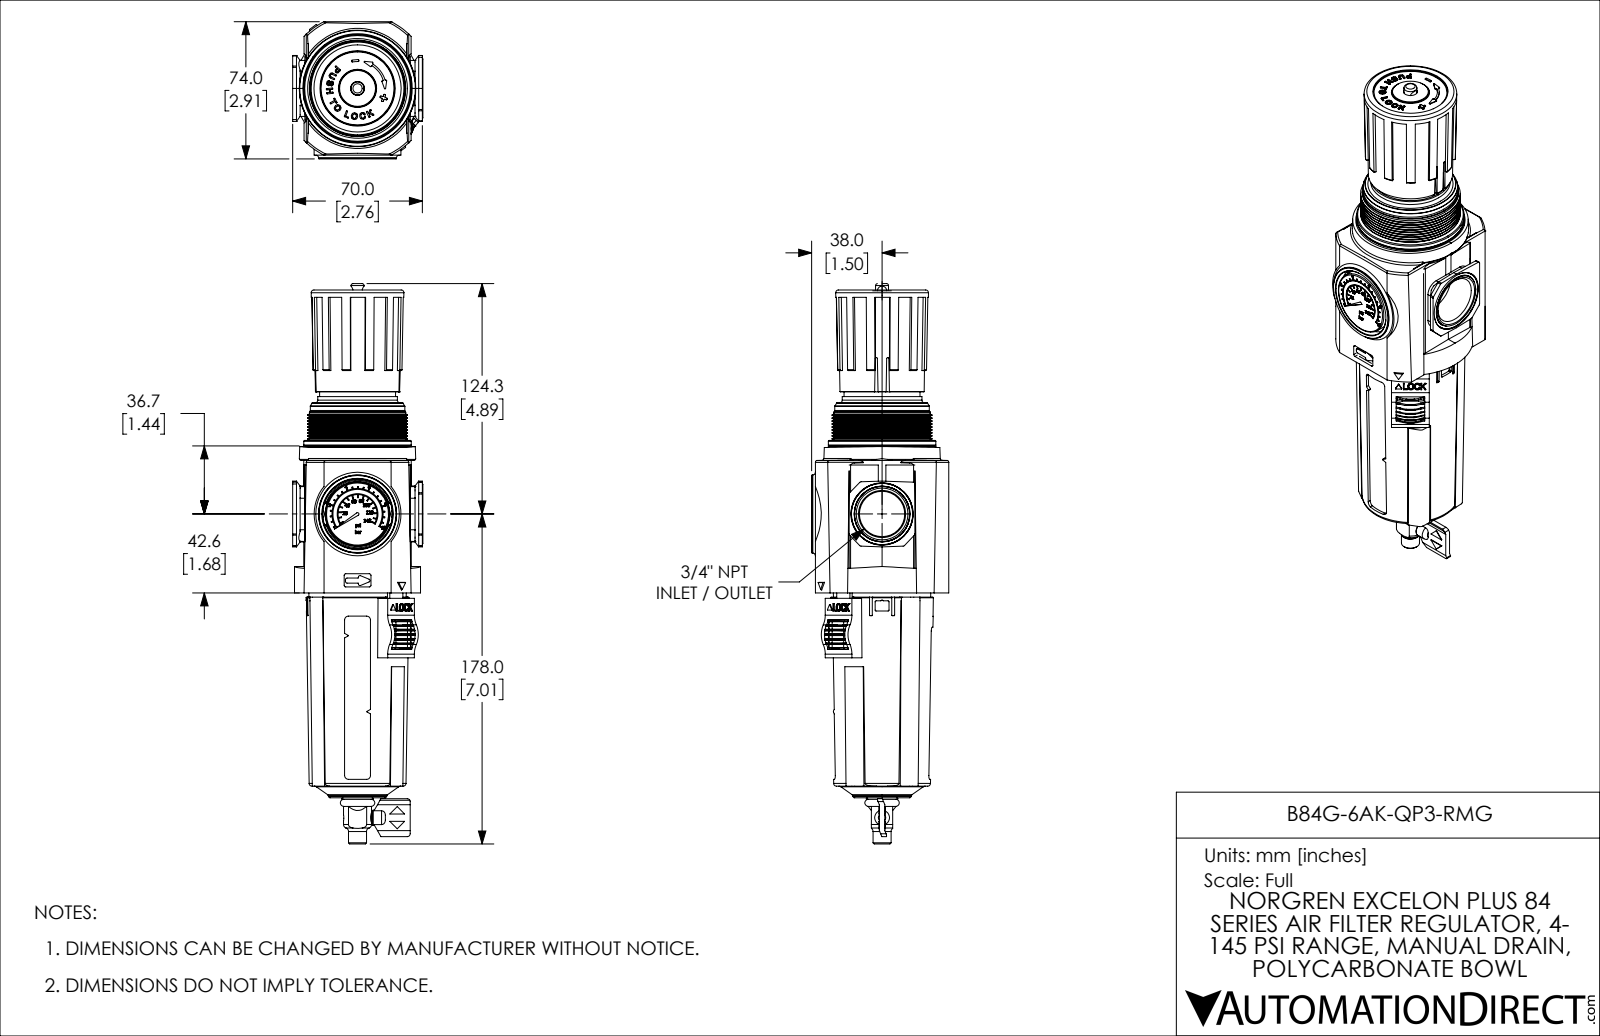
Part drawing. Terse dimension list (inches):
name: B84G-6AK-QP3-RMG
written by: SolidWorks 2021 (CONFIG_CONTROL_DESIGN)
unit: in
bodies: 8 solids, 2537 faces (932 planar, 1170 cylindrical, 435 other)
size: 11.9 × 2.913 × 2.766
volume: 45.46 in³; area: 208.5 in²
holes: 2× ⌀0.177, 1× ⌀0.059, 1× ⌀0.123, 1× ⌀0.126, 1× ⌀0.197, 1× ⌀0.236, 1× ⌀0.25, 1× ⌀0.374, 1× ⌀0.969, 1× ⌀1.319, 1× ⌀2.323, 1× ⌀2.461
bosses: 2× ⌀0.299, 2× ⌀0.157, 1× ⌀2.283, 1× ⌀2.119, 1× ⌀2.047, 1× ⌀2.026, 1× ⌀2.008, 1× ⌀1.693
rounds: 27× R0.012, 26× R0.02, 24× R0.01, 23× R0.039, 18× R0.047, 16× R0.028, 16× R0.03, 14× R0.004
face distances: 2.719, 2.323, 0.035, 2.683, 0.622, 0.512, 2.096, 2.061, 3.866, 3.831
hole spacings: 0.856, 1.713, 11.189
